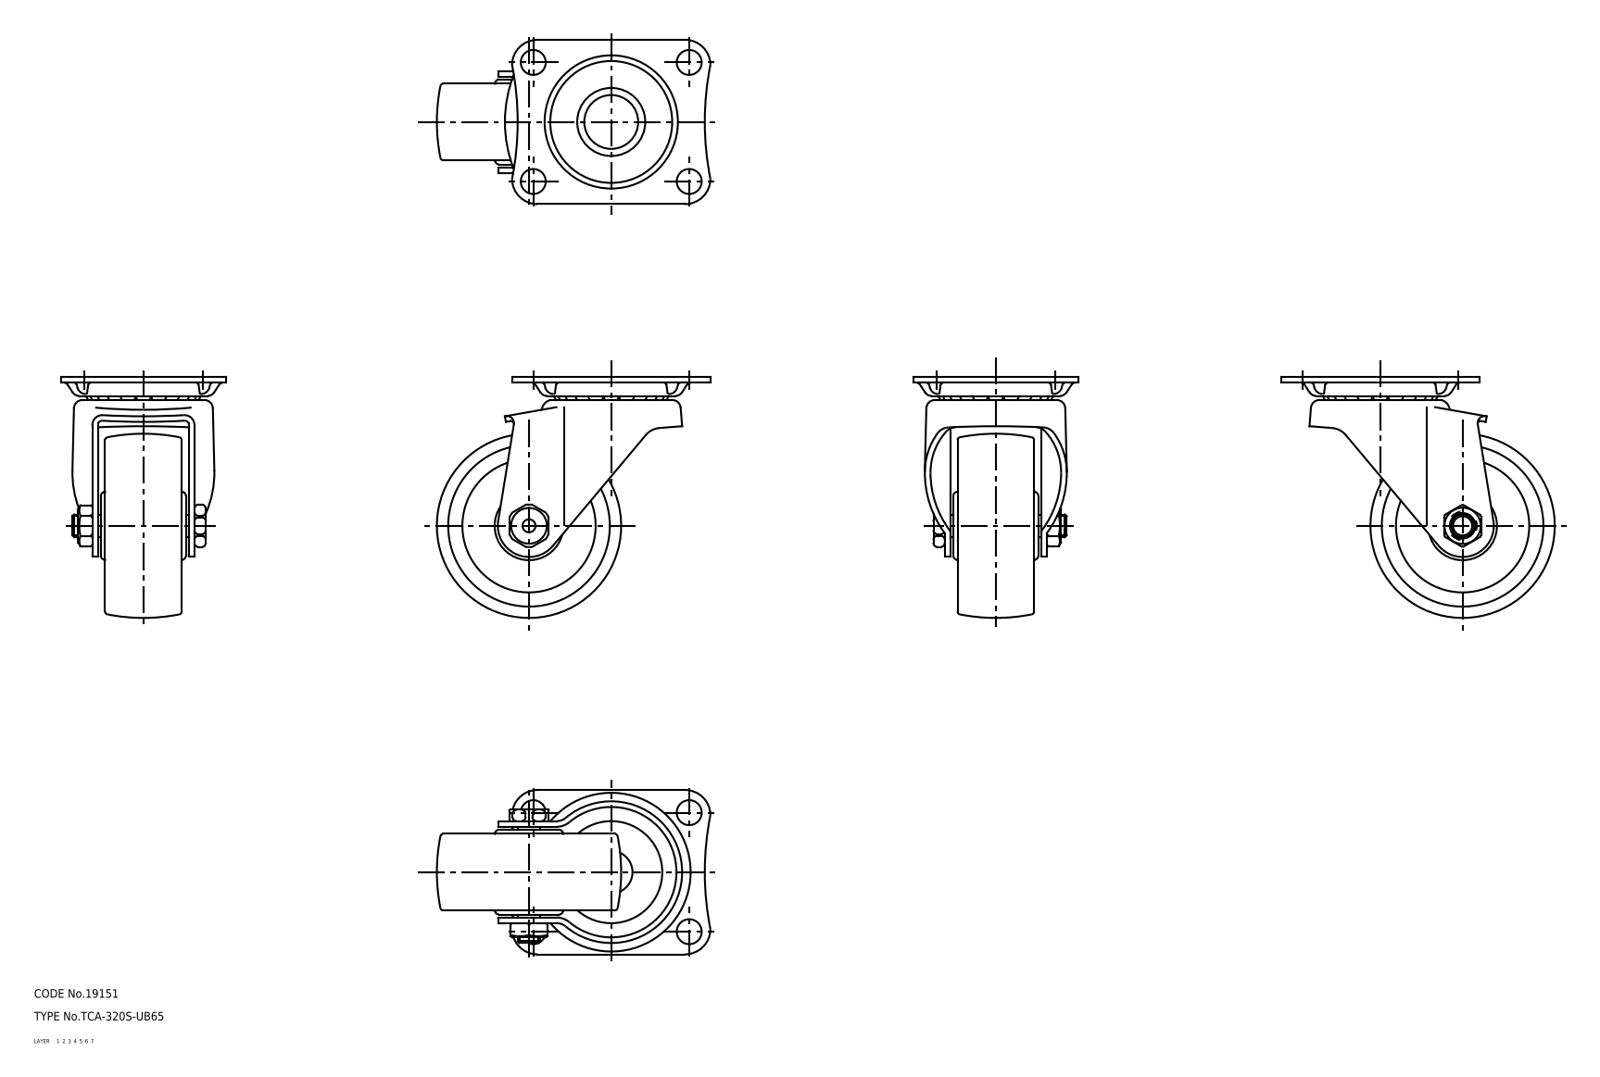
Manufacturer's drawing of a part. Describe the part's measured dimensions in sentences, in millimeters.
The part is named "wheel; mounting plate; main shaft; axle (+1 more)". Its 3-D file was written by "CADfix (AUTOMOTIVE_DESIGN)". It is 5 solids with 337 faces: 0 planar, 0 cylindrical and 337 other. Overall it measures 96.5 by 85 by 58 millimeters. Its volume is 106 770 cubic millimeters and its surface area 42 203 square millimeters.
